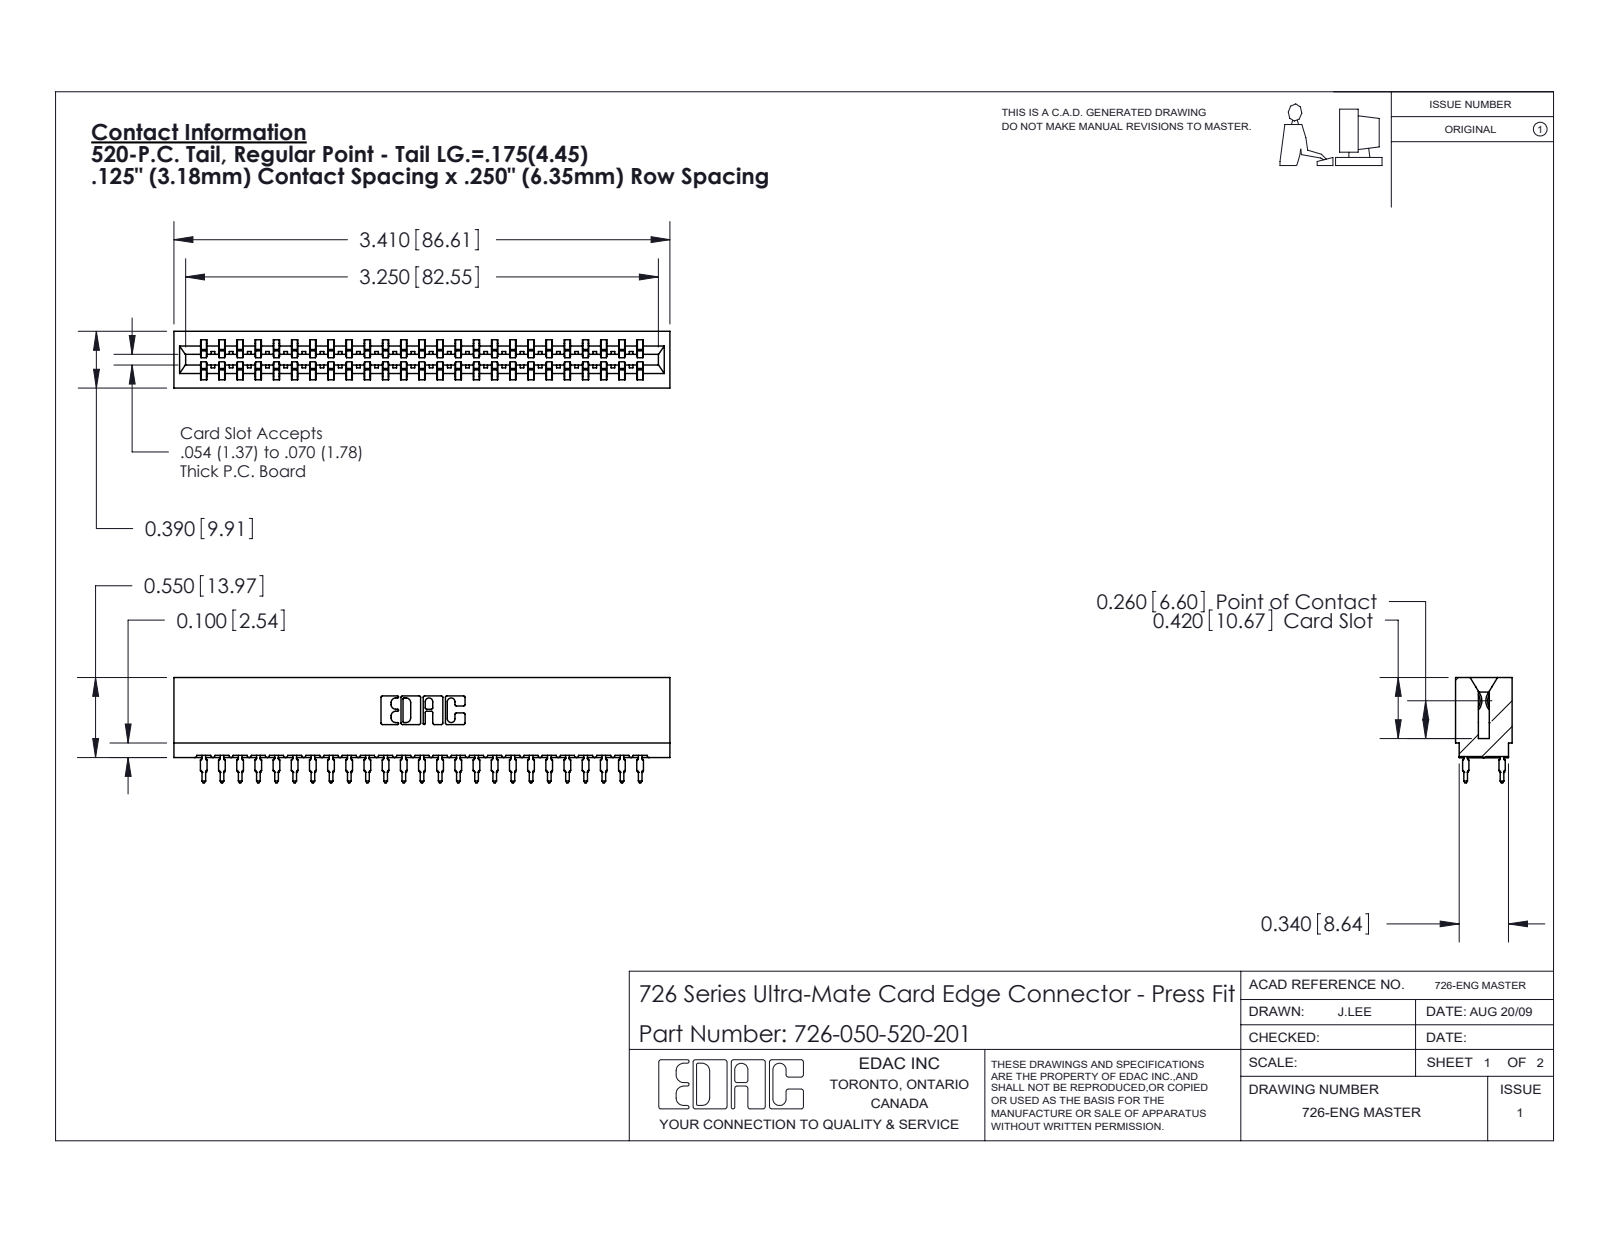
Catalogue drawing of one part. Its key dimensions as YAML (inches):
part_name: "726 Part_.515 Slot Depth - 01; 726-050-520-201; 746-292-001_520"
step_written_by: "SolidWorks 2020 (CONFIG_CONTROL_DESIGN)"
units: inches
bodies: {solids: 51, faces: 4572, planar: 2355, cylindrical: 917, other: 1300}
overall_size: [3.41, 0.724, 0.39]
volume: 0.489
surface_area: 19.91
partial_cylinders:
  - {radius: 0.021, count: 100}
  - {radius: 0.015, count: 26}
  - {radius: 0.01, count: 22}
  - {radius: 0.005, count: 8}
  - {radius: 0.011, count: 8}
  - {radius: 0.007, count: 6}
  - {radius: 0.031, count: 6}
  - {radius: 0.026, count: 3}
face_to_face_distances: [0.057, 0.333, 0.25, 0.39, 0.025, 0.307, 0.275, 0.083, 0.75, 0.5]
